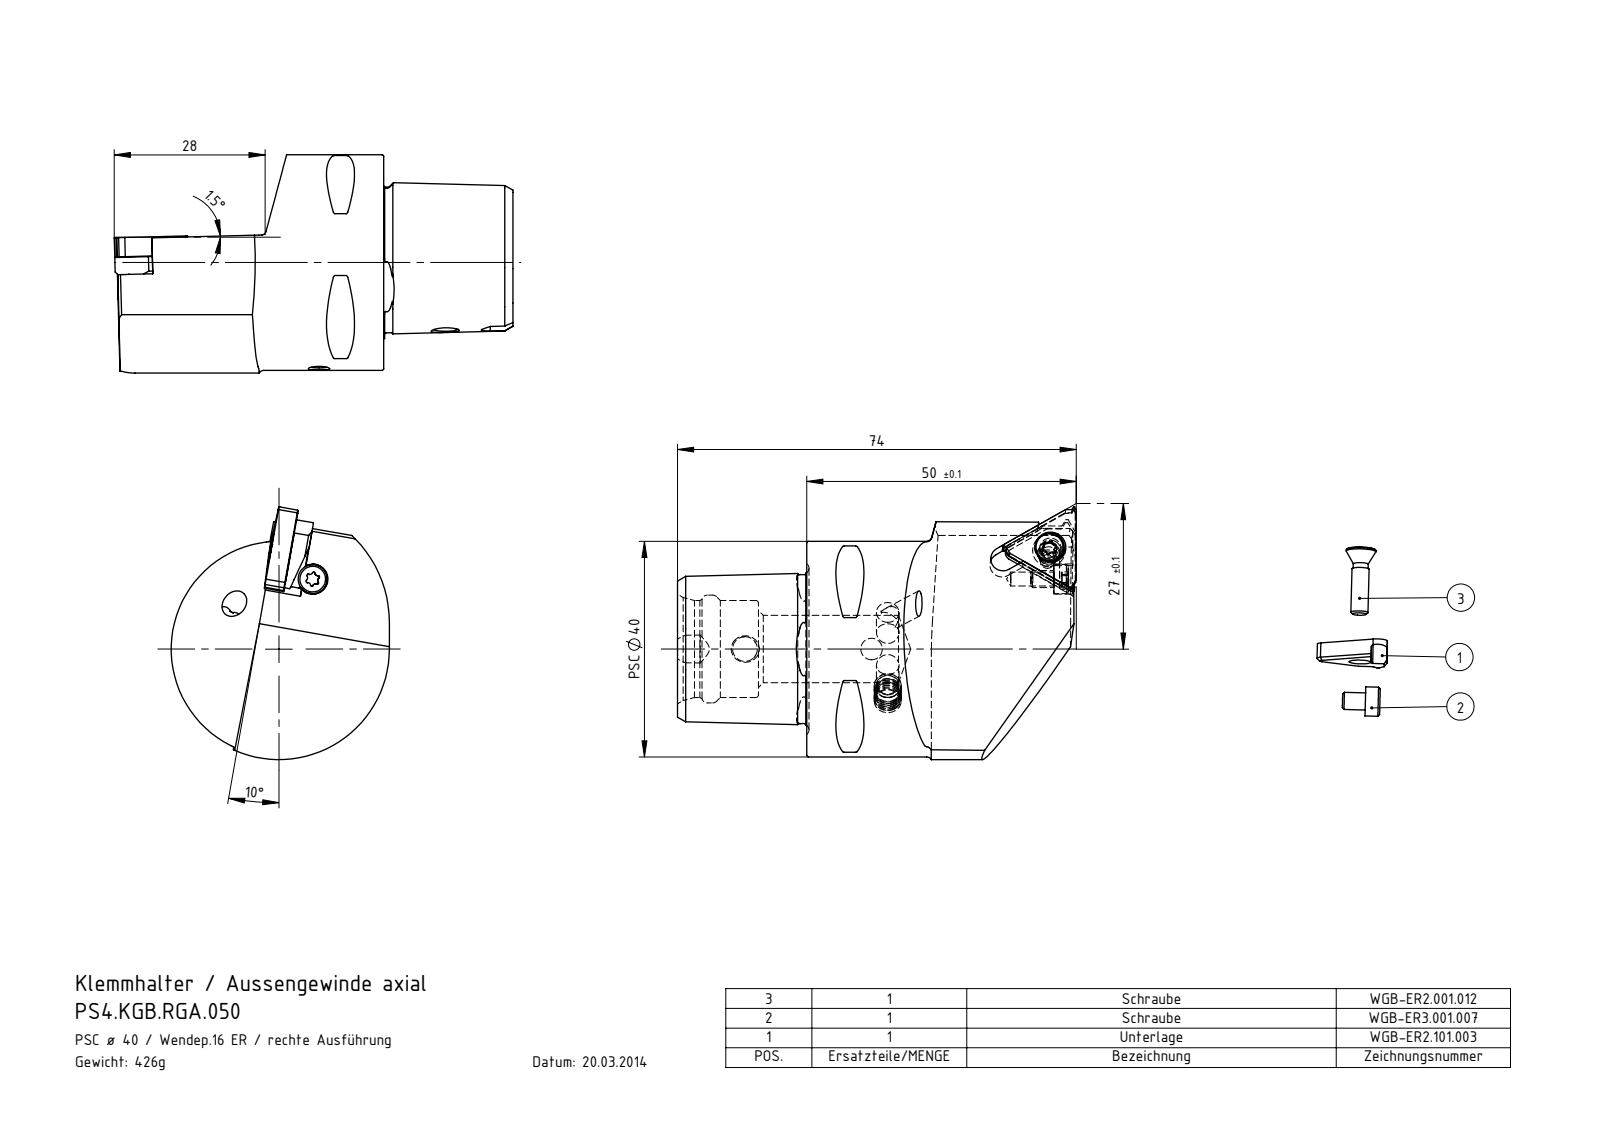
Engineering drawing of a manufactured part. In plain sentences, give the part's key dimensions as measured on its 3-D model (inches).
The part is named "KVT_MB_600_050; PS4.KGB.RGA.050; WGB-ER2.001.012_A; LT16EL (+4 more)". Its 3-D file was written by "SolidWorks 2017 (AUTOMOTIVE_DESIGN)". It is 7 solids with 335 faces: 88 planar, 103 cylindrical and 144 other. Overall it measures 2.913 by 1.847 by 1.594 inches. Its volume is 3.293 cubic inches and its surface area 21.67 square inches. Round holes: 3 of diameter 0.157, 2 of diameter 0.102, 2 of diameter 0.165, 1 of diameter 0.158, 1 of diameter 0.181, 1 of diameter 0.197, 1 of diameter 0.492, 1 of diameter 0.709, 1 of diameter 0.787. Round bosses or shafts: 2 of diameter 0.217, 1 of diameter 1.575, 1 of diameter 0.197, 1 of diameter 0.125, 1 of diameter 0.118, 1 of diameter 0.109. Partial cylindrical surfaces (rounded edges, fillets, slot ends): 8 of radius 0.012, 6 of radius 0.009, 6 of radius 0.013, 6 of radius 0.022, 6 of radius 0.022, 2 of radius 0.004, 2 of radius 0.01, 1 of radius 0.031. The main face-to-face distances are 0.945, 0.262, 0.611, 0.144, 0.126, 0.136, 0.27, 1.39, 0.126, 0.136. The hole center spacings are 0.925.
